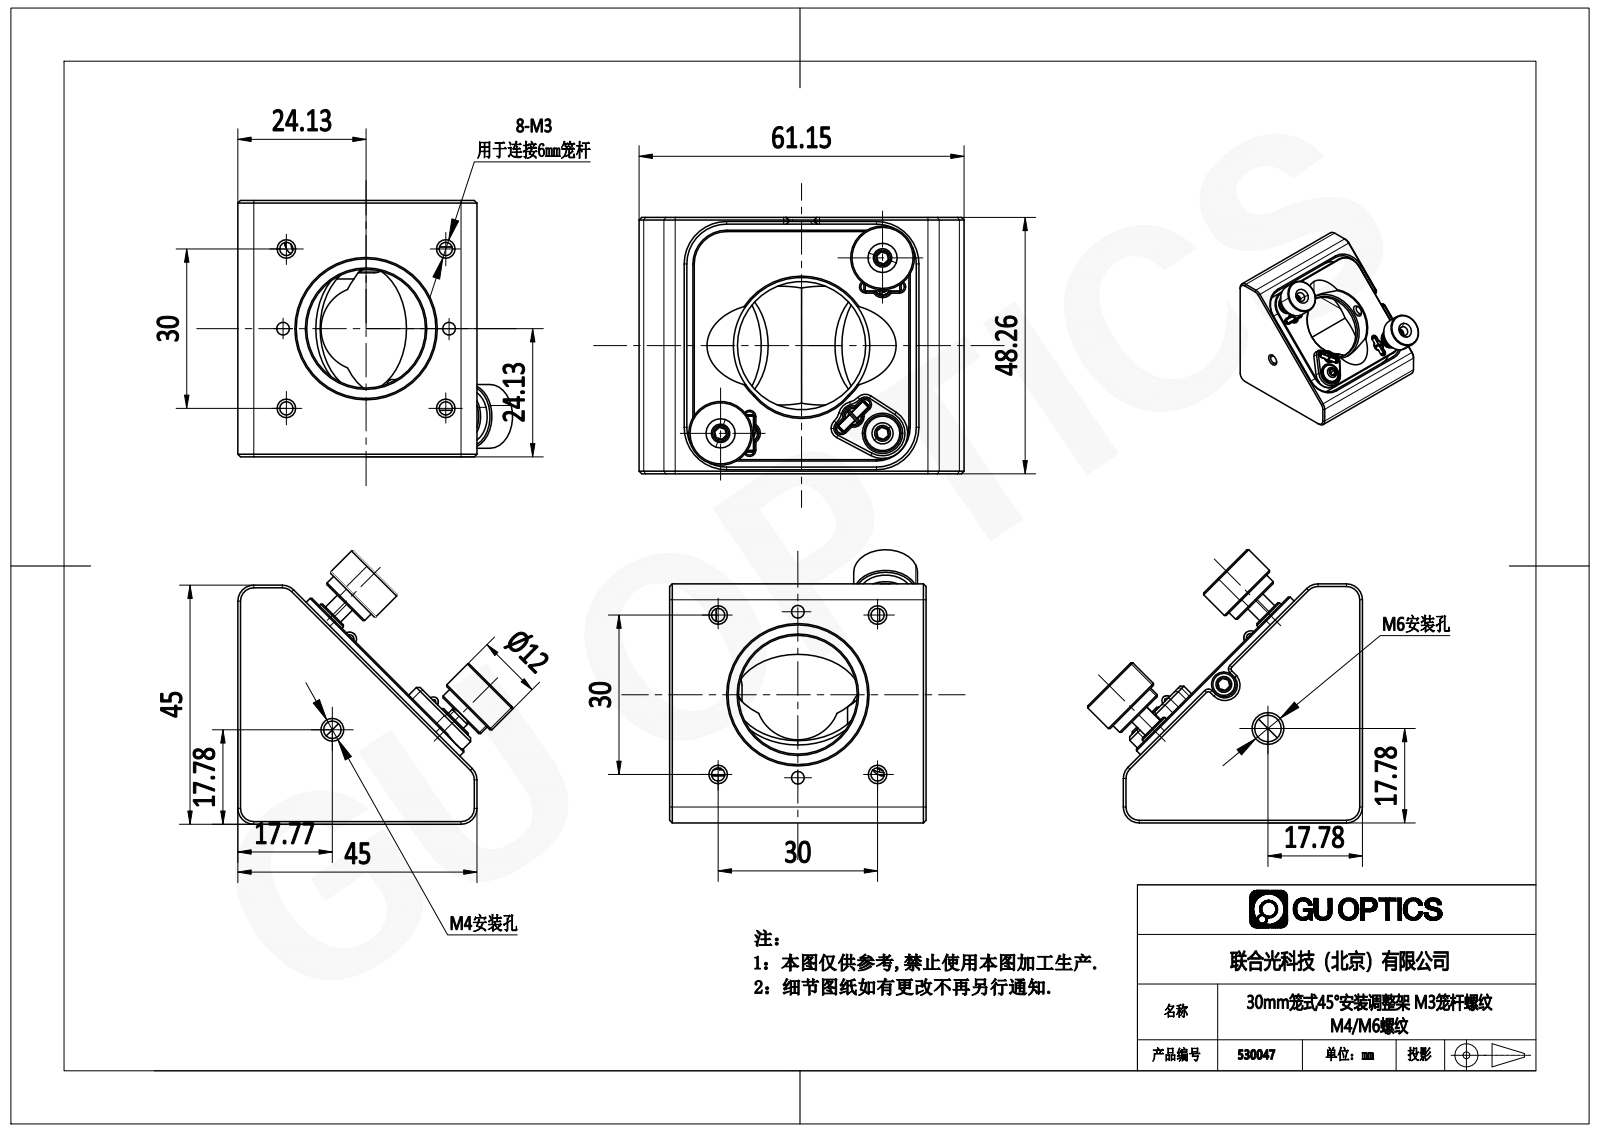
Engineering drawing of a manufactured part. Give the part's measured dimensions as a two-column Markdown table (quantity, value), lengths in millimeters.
| quantity | value |
| --- | --- |
| part name | 2.2.3.7_L30T-ZM-A_30 mm笼式系统直角光学调整架，带M3笼杆螺纹，带M4，M6螺纹 |
| STEP written by | SolidWorks 2018 (AUTOMOTIVE_DESIGN) |
| units | millimeters |
| bodies | 0 solids, 391 faces (104 planar, 124 cylindrical, 163 other) |
| overall size | 51.7 × 51.42 × 48.26 |
| round holes (diameter × count) | 2.5 × 8, 2.4 × 4, 3.56 × 3, 3.5 × 2, 3.75 × 2, 22.35 × 2, 27.29 × 2, 3.3 × 1, 4.17 × 1, 5 × 1, 24.13 × 1, 26.29 × 1 |
| round bosses / shafts (diameter × count) | 4 × 3, 1.5 × 3, 12 × 2, 10 × 2, 6 × 2, 7 × 1 |
| partial cylindrical surfaces (radius × count) | 0.93 × 6, 3 × 5, 6.35 × 4, 7.49 × 4, 1 × 2, 1.94 × 2, 3.17 × 2, 7.94 × 2 |
| main face-to-face distances | 48.26, 2.58, 9.69, 7.11, 45, 1.27, 1.14, 46.99, 3.81, 2.41 |
| hole center spacings | 15.01, 21.21, 30, 34.1, 15.62, 42.43, 22.47, 31.24 |
